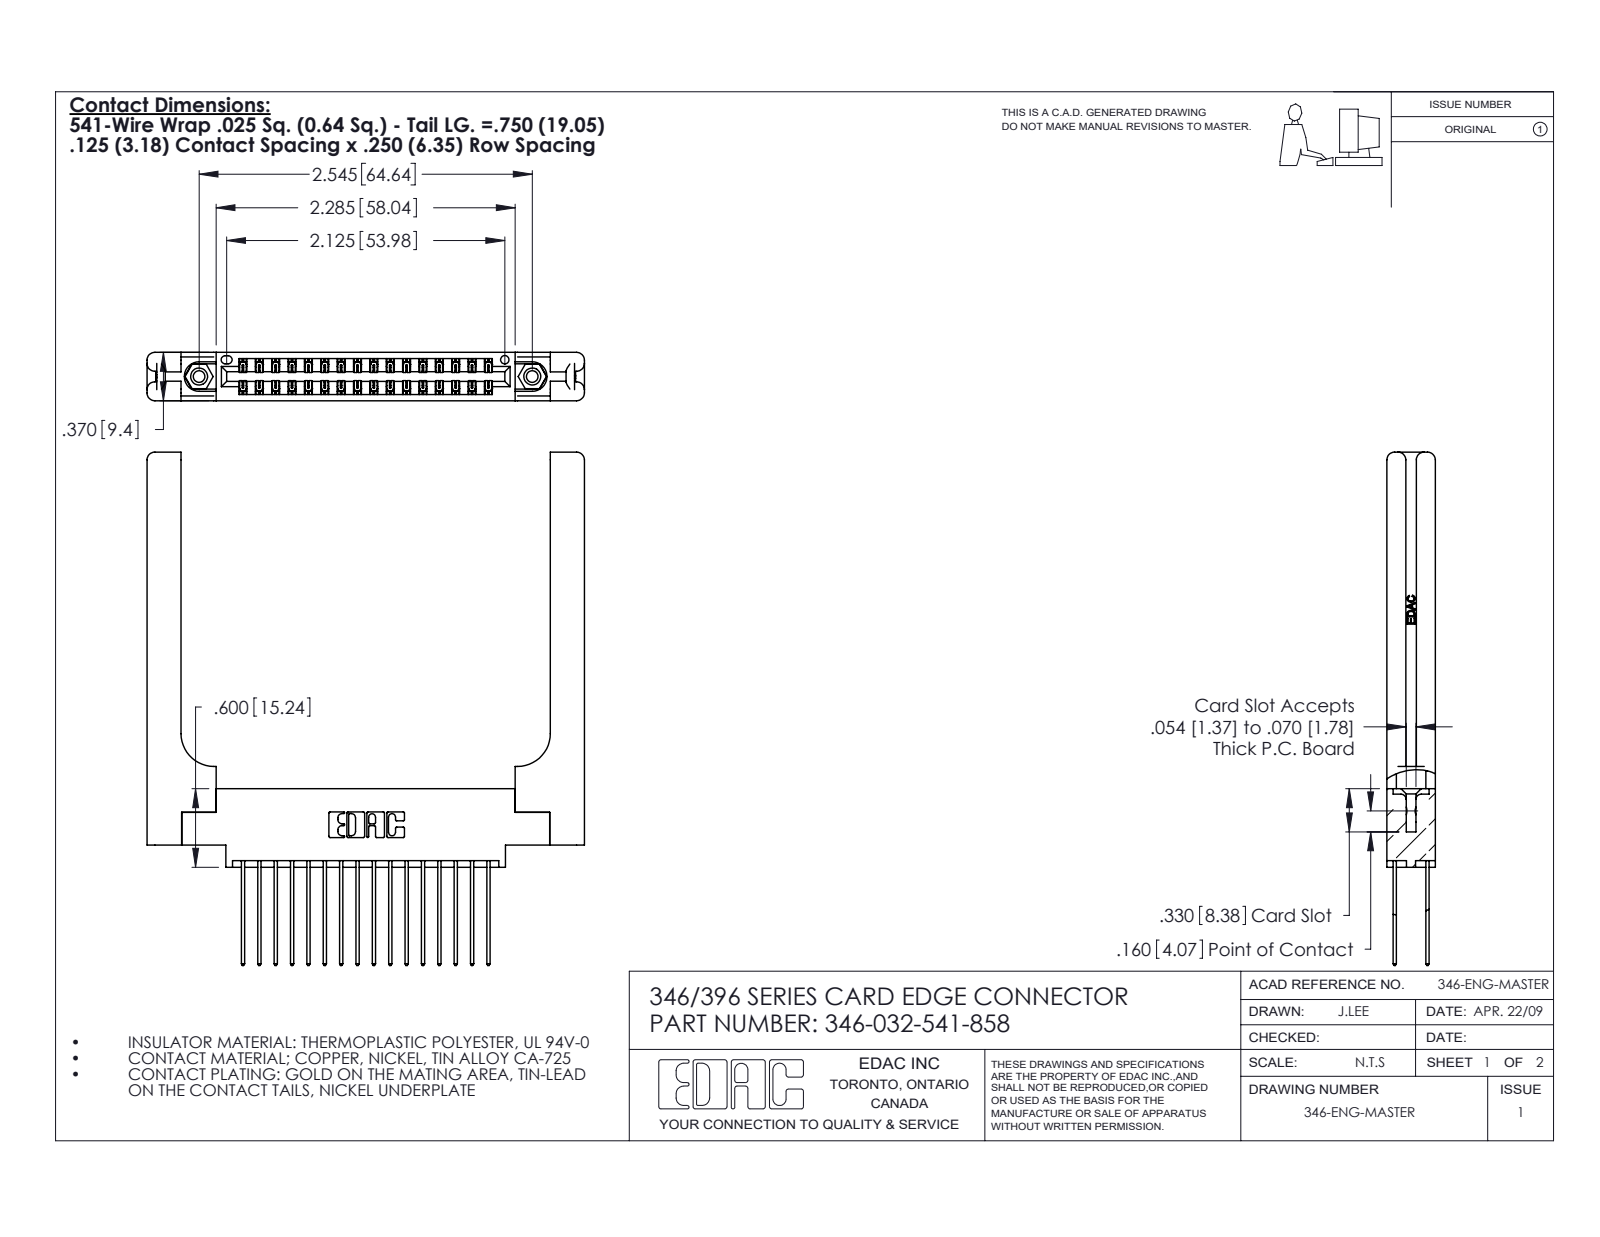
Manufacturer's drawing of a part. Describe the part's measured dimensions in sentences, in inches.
The part is named "346-032-541-858; 346-220-058_345-220-058; 345-292-001_345-293-141; 345-250-001_345-250-001-102 (+1 more)". Its 3-D file was written by "SolidWorks 2020 (CONFIG_CONTROL_DESIGN)". It is 37 solids with 2060 faces: 1362 planar, 638 cylindrical and 60 other. Overall it measures 3.92 by 3.341 by 0.37 inches. Its volume is 0.951 cubic inches and its surface area 25.99 square inches. Round holes: 2 of diameter 0.089, 2 of diameter 0.125, 2 of diameter 0.156, 1 of diameter 0.064. Round bosses or shafts: 2 of diameter 0.155. Partial cylindrical surfaces (rounded edges, fillets, slot ends): 48 of radius 0.006, 32 of radius 0.01, 22 of radius 0.01, 16 of radius 0.06, 6 of radius 0.007, 6 of radius 0.031, 3 of radius 0.026, 2 of radius 0.014. The main face-to-face distances are 0.37, 0.072, 0.048, 0.322, 0.148, 0.15, 0.25, 0.025, 0.298, 0.077. The hole center spacings are 0.246, 2.338, 2.545.
